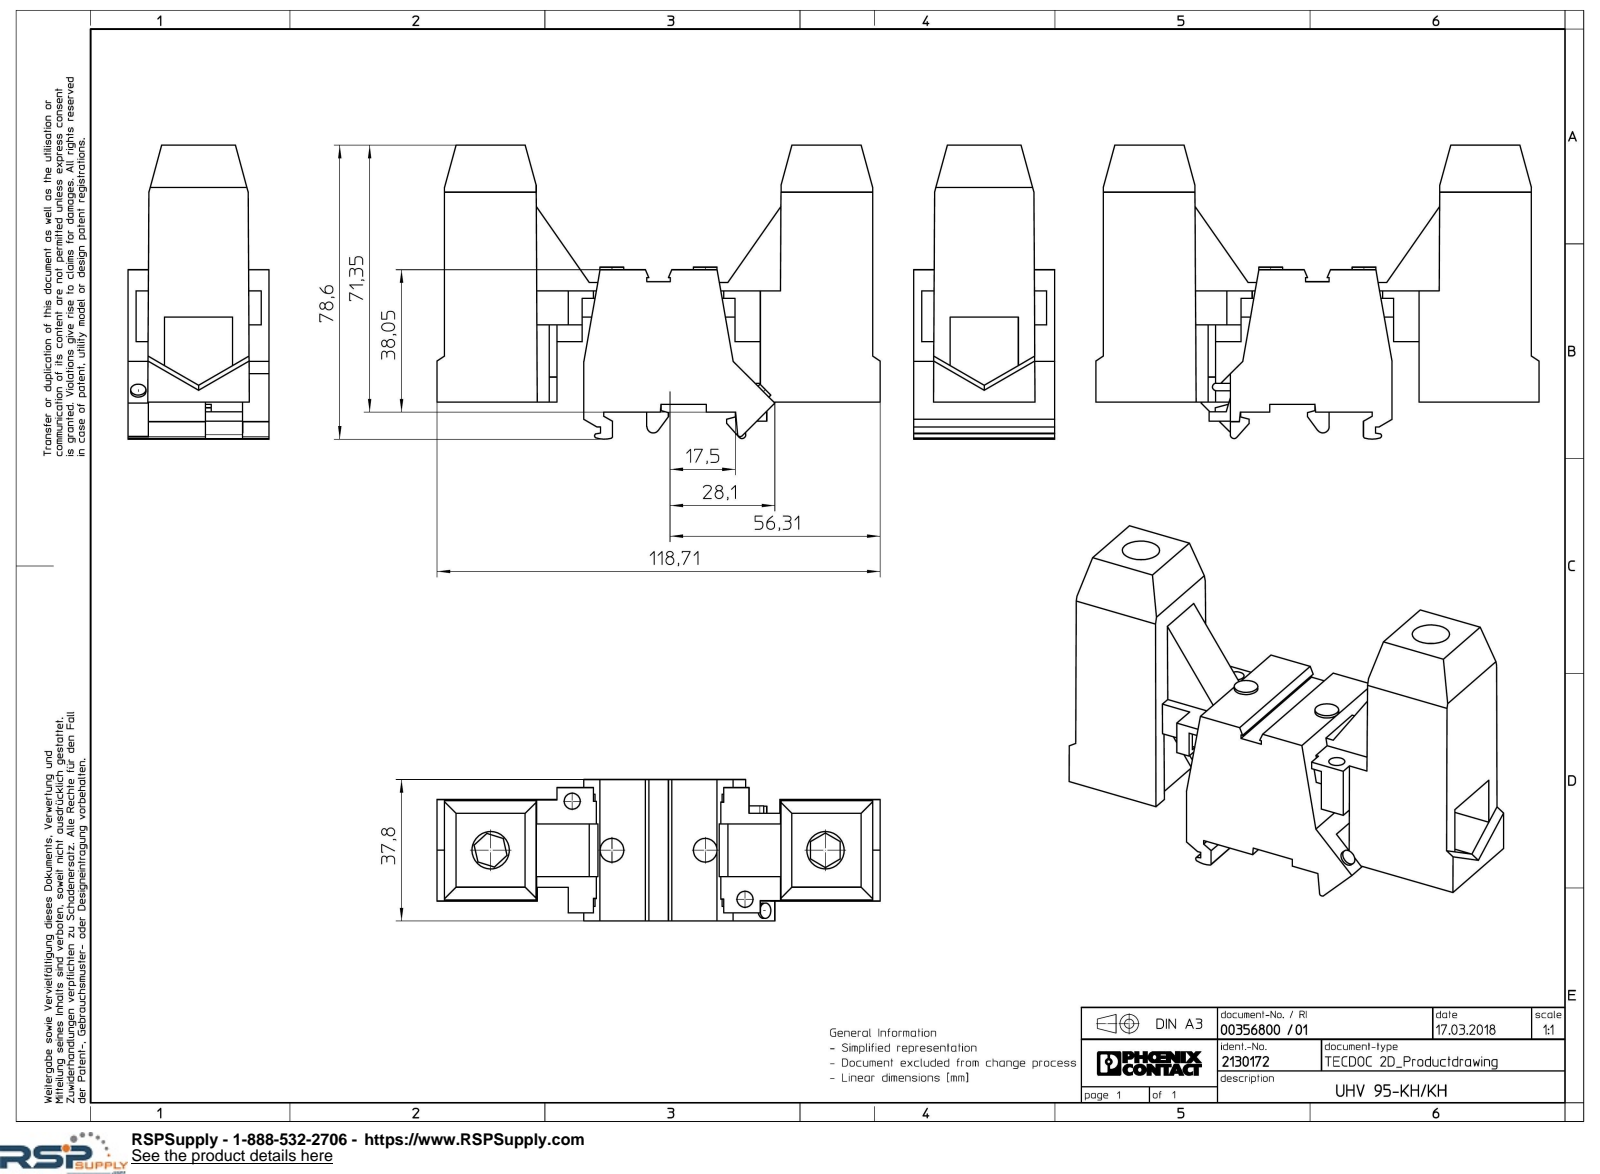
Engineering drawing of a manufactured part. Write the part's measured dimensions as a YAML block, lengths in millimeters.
part_name: "UHV_95_KH_KH_select"
step_written_by: "Creo Elements/Direct Modeling 18.1I 14-Aug-2016 (C) Parametric Technology GmbH (AUTOMOTIVE_DESIGN)"
units: millimeters
bodies: {solids: 1, faces: 263, planar: 237, cylindrical: 22, other: 4}
overall_size: [118.71, 78.6, 37.8]
volume: 142178
surface_area: 35903
round_holes:
  - {diameter: 4.3, count: 2}
  - {diameter: 10, count: 2}
round_bosses_or_shafts:
  - {diameter: 6.35, count: 2}
  - {diameter: 4.11, count: 1}
partial_cylinders:
  - {radius: 0.5, count: 3}
  - {radius: 1, count: 2}
  - {radius: 0.63, count: 1}
  - {radius: 1.7, count: 1}
  - {radius: 7.2, count: 1}
face_to_face_distances: [37.8, 22.75, 2, 30.1, 86.61, 114.71, 22.7, 92.01, 2.65, 35.4]
hole_center_spacings: [25.22, 25.48, 53.19, 69.09, 69.39, 89.69]
